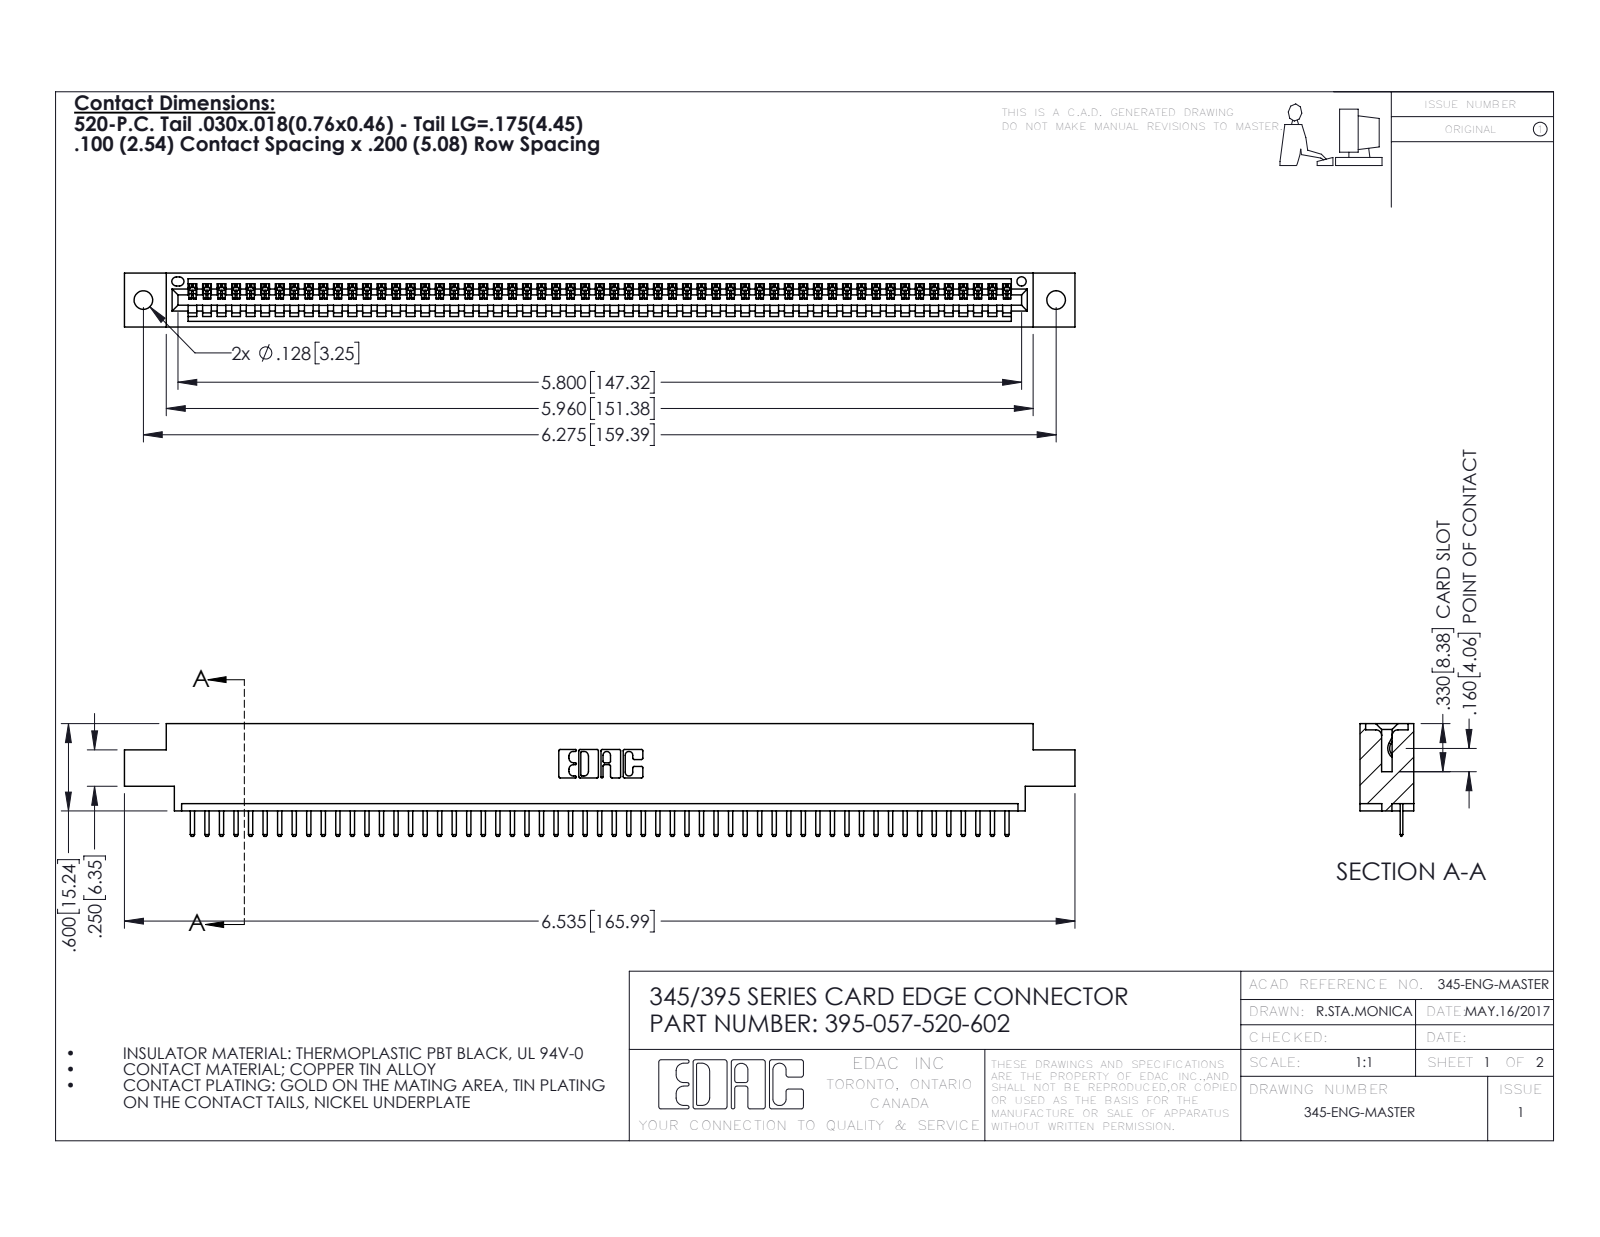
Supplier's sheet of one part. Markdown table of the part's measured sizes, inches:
| quantity | value |
| --- | --- |
| part name | 345-292-001_345-293-120; 395-057-520-602; 345 Part_0.170 Offset - 0.128 Dia |
| STEP written by | SolidWorks 2016 (CONFIG_CONTROL_DESIGN) |
| units | inches |
| bodies | 58 solids, 3664 faces (2478 planar, 1186 cylindrical, 0 other) |
| overall size | 6.535 × 0.775 × 0.37 |
| volume | 0.95 in³ |
| surface area | 31.34 in² |
| round holes (diameter × count) | 0.128 × 2, 0.064 × 1 |
| partial cylindrical surfaces (radius × count) | 0.01 × 116, 0.006 × 114, 0.01 × 22, 0.007 × 6, 0.031 × 6, 0.026 × 3, 0.031 × 2, 0.04 × 2 |
| main face-to-face distances | 0.298, 0.072, 0.37, 0.2, 0.098, 0.272, 0.025, 0.225, 0.072, 0.175 |
| hole center spacings | 0.27, 6.039, 6.275 |
